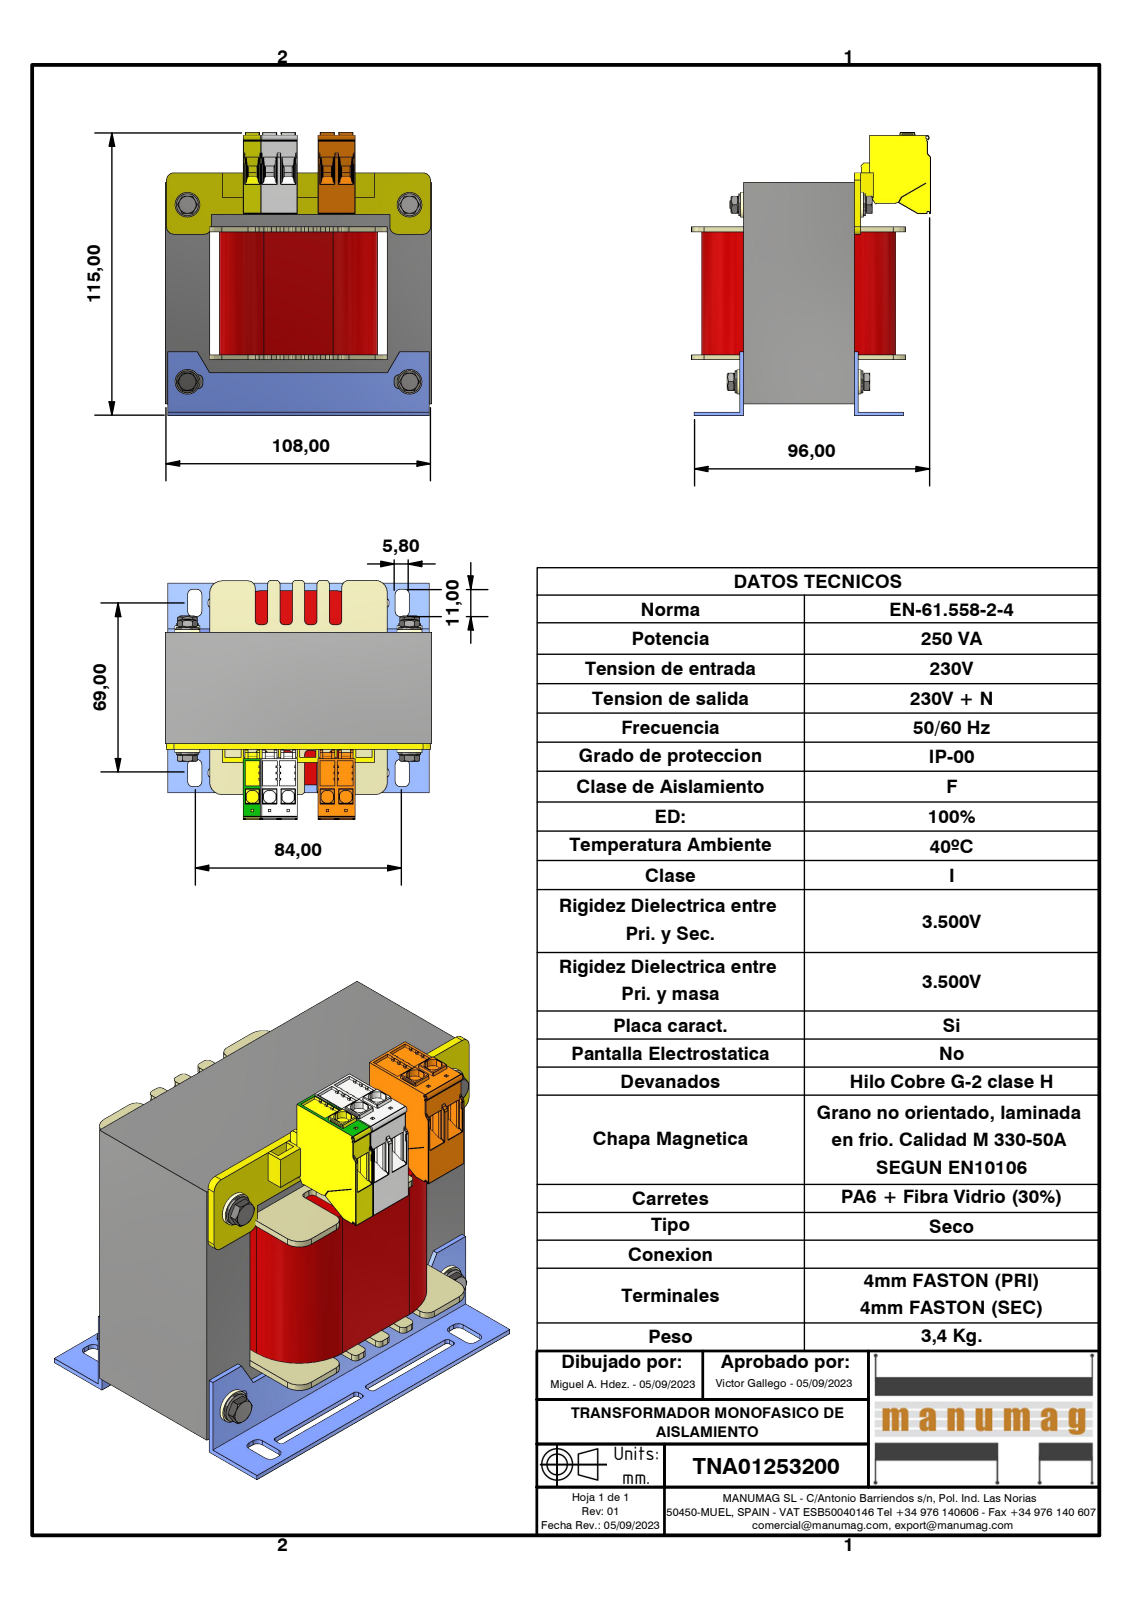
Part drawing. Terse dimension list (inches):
name: TNA01253200; EI108 x 90 - 45 (RC36); AF36DIN; EI108 (+8 more)
written by: Autodesk Inventor 2023 (AUTOMOTIVE_DESIGN)
unit: in
bodies: 32 solids, 5256 faces (4294 planar, 658 cylindrical, 304 other)
size: 4.538 × 4.252 × 3.825
volume: 34.23 in³; area: 203.2 in²
holes: 4× ⌀0.128, 4× ⌀0.157, 4× ⌀0.169, 4× ⌀0.22
bosses: 4× ⌀0.394, 4× ⌀0.354, 4× ⌀0.232, 4× ⌀0.193, 4× ⌀0.143
rounds: 214× R0.006, 58× R0.008, 28× R0.059, 24× R0.079, 20× R0.039, 14× R0.02, 10× R0.118, 10× R0.197
face distances: 0.709, 2.835, 1.417, 1.772, 2.126, 3.543, 0.059, 1.969, 0.866, 0.157
hole spacings: 2.835, 3.543, 4.538
